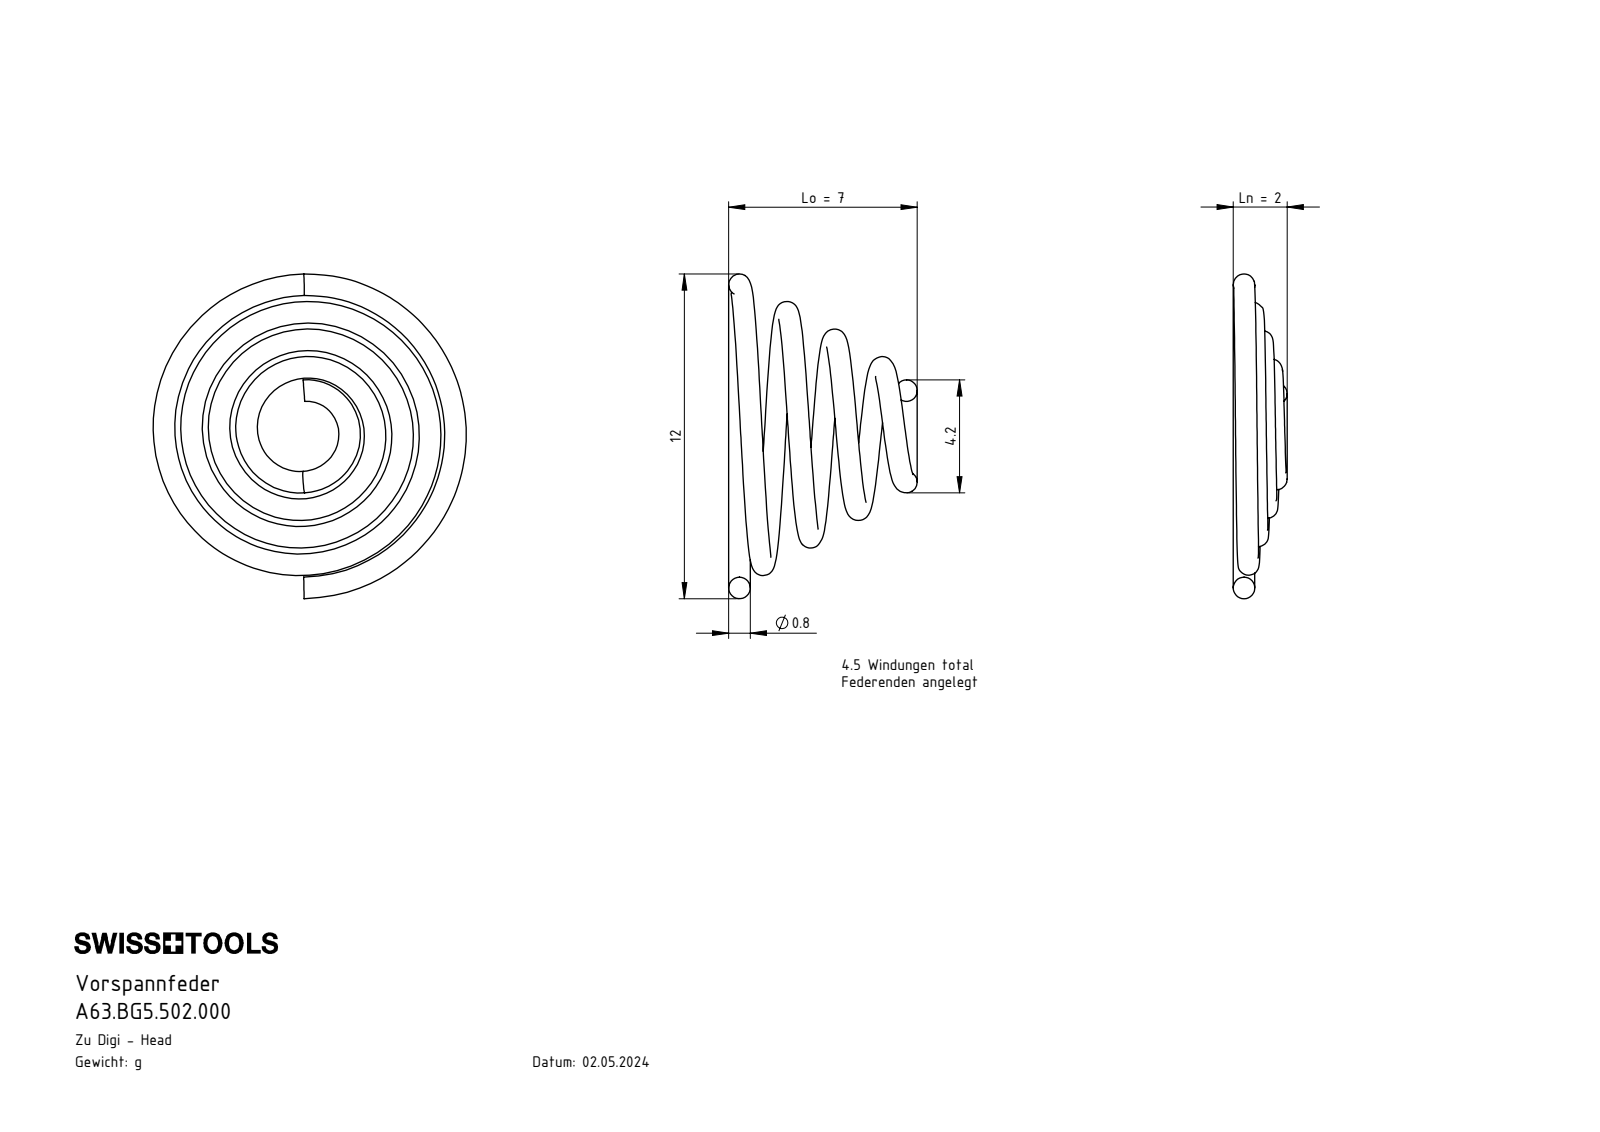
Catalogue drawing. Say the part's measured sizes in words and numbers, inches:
The part is named "A63.BG5.502.000". Its 3-D file was written by "SolidWorks 2017 (AUTOMOTIVE_DESIGN)". It is 1 solid with 8 faces: 2 planar, 0 cylindrical and 6 other. Overall it measures 0.474 by 0.457 by 0.276 inches. Its volume is 0.003 cubic inches and its surface area 0.406 square inches.
